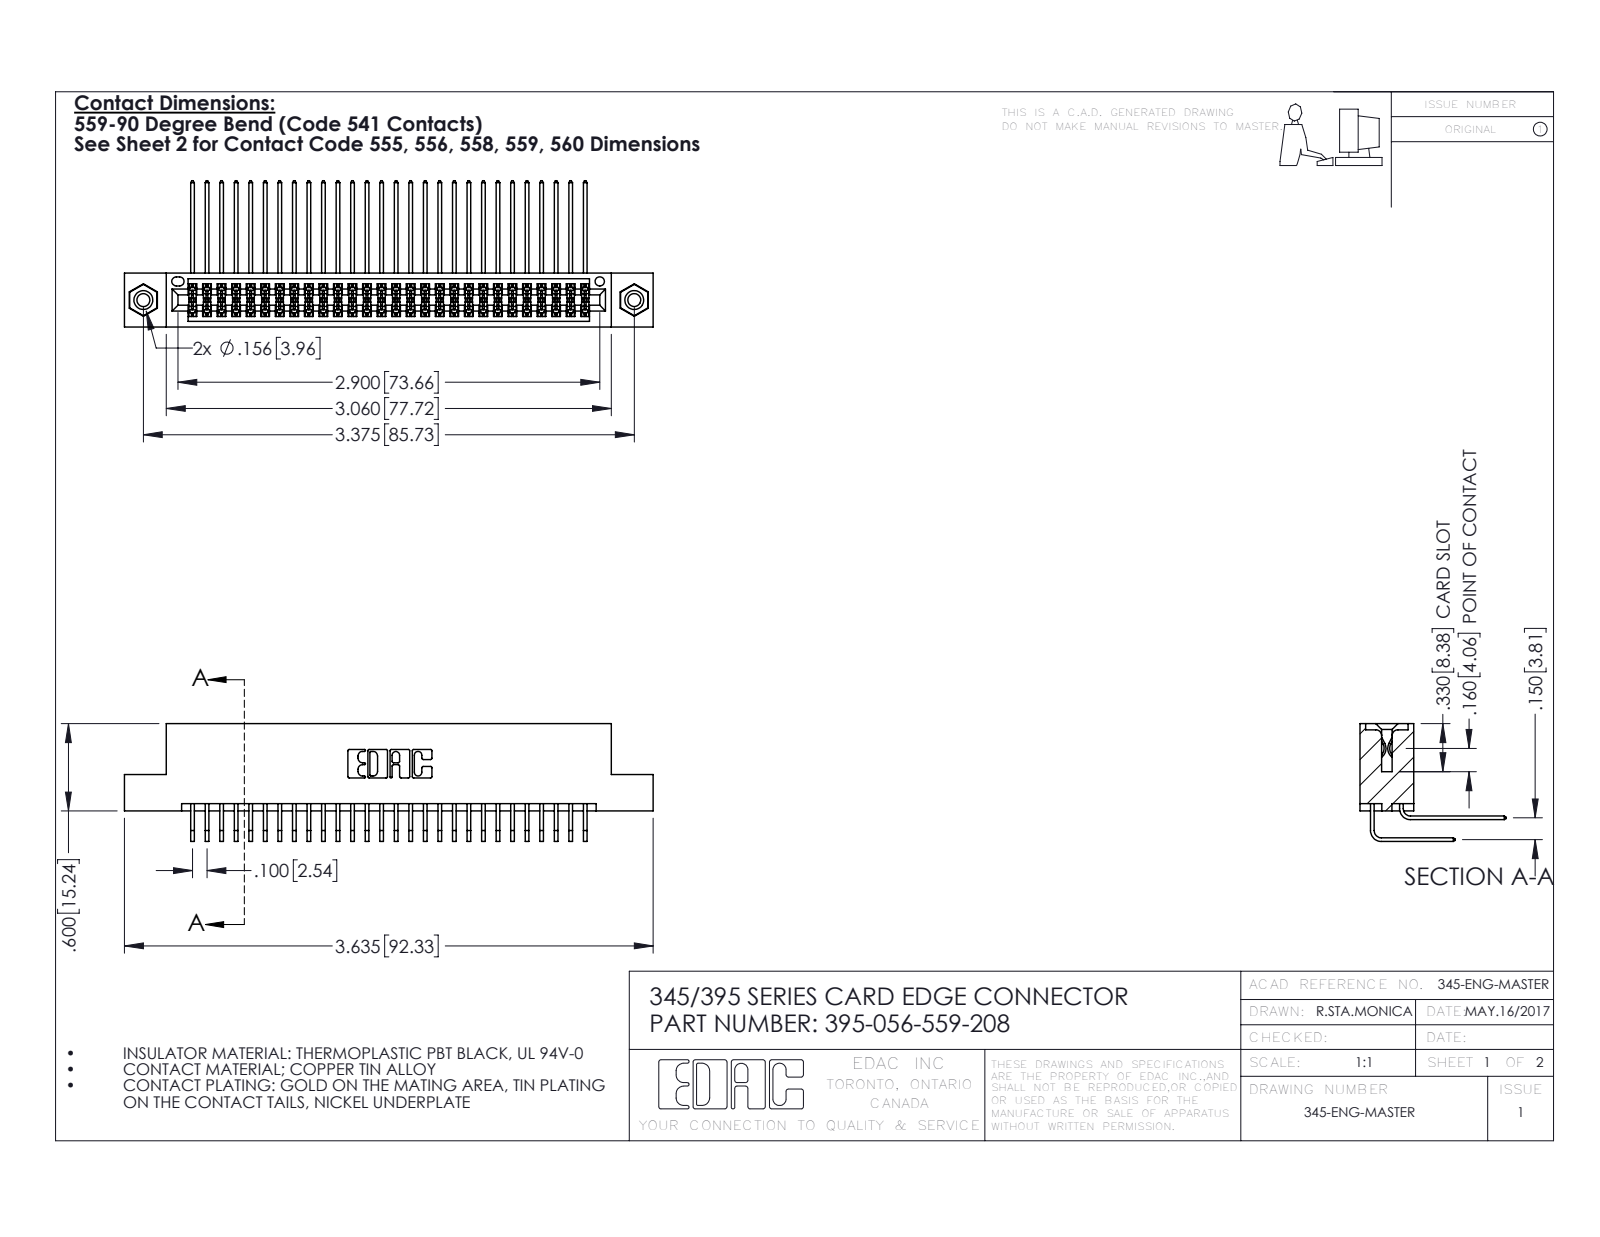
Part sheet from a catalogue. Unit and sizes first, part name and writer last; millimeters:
Units: millimetres
Overall size (bounding box): 92.3 × 25.5 × 20.5
Round holes (diameter × count): ⌀2.3 ×2, ⌀3.2 ×2, ⌀4 ×2, ⌀1.6 ×1
Round bosses / shafts (diameter × count): ⌀3.9 ×2
Partial cylindrical surfaces — rounded edges, fillets, slot ends (radius × count): R0.2 ×111, R0.3 ×22, R0.2 ×6, R0.8 ×6, R0.7 ×3, R0.4 ×2, R0.5 ×2, R0.6 ×2
Main face-to-face distances: 1.8, 7.6, 5.1, 9.4, 2.5, 6.9, 0.6, 5.7, 3.8, 4.4
Hole centre spacings: 6.9, 79.8, 85.7
Volume: 9 160 mm³ · Surface area: 14 790 mm²
Bodies: 59 solids, 3098 faces (2072 planar, 1010 cylindrical, 16 other)
Part name (STEP PRODUCT): 345-250-001_345-250-003-102; 345-292-001_558 559 Tail - 1; 345 Part_Flush Mounting Lugs - 0.156 Dia-TI; 345-292-001_559 Tail - 2 (+1 more)
STEP written by: SolidWorks 2016 (CONFIG_CONTROL_DESIGN)
